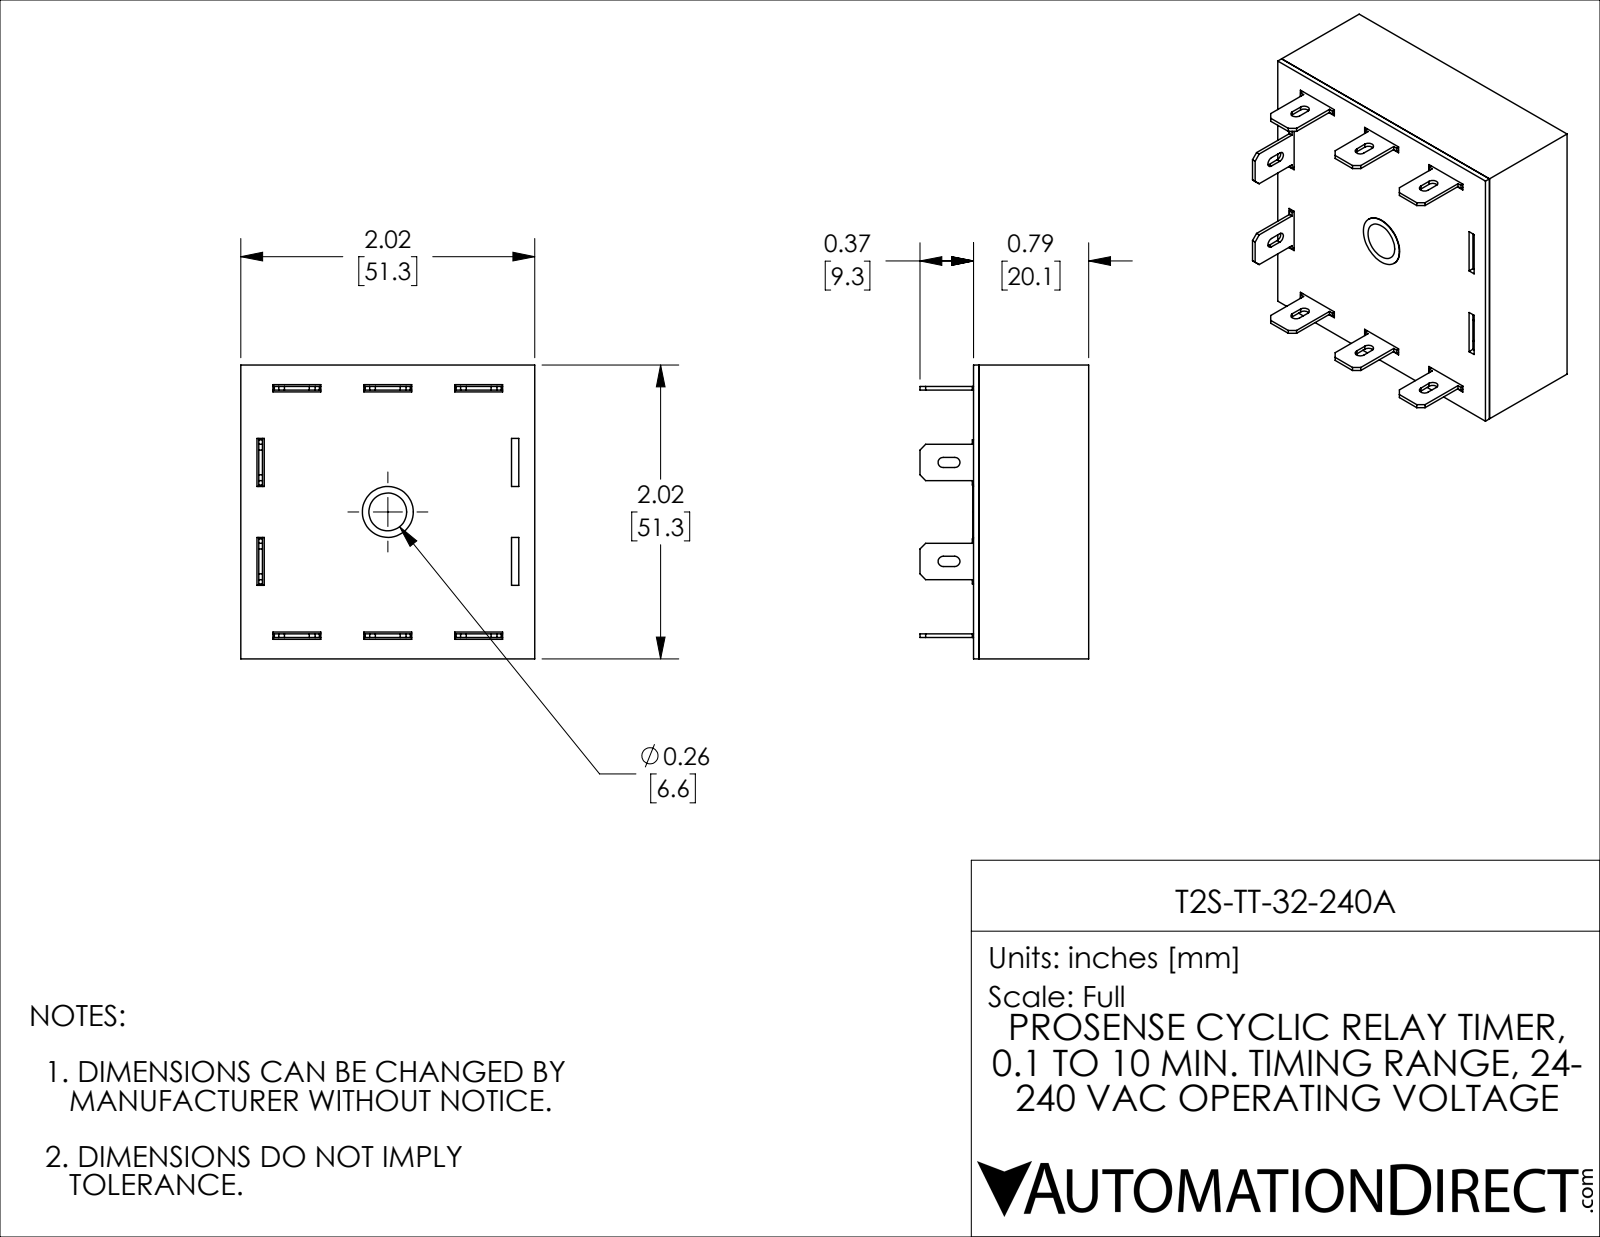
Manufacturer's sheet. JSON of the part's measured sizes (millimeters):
{"part_name": "T2S-TT-32-240A", "step_written_by": "SolidWorks 2021 (CONFIG_CONTROL_DESIGN)", "units": "millimeters", "bodies": {"solids": 10, "faces": 256, "planar": 234, "cylindrical": 20, "other": 2}, "overall_size": [51.31, 51.31, 29.46], "volume_mm3": 11042, "surface_area_mm2": 22819, "round_holes": [[8.89, 1]], "partial_cylinders_radius": [[0.89, 10]], "face_to_face_distances": [1.14, 50.16, 19.15, 20.12, 0.97, 18.01, 18.98, 51.3, 49.02, 3.74]}
